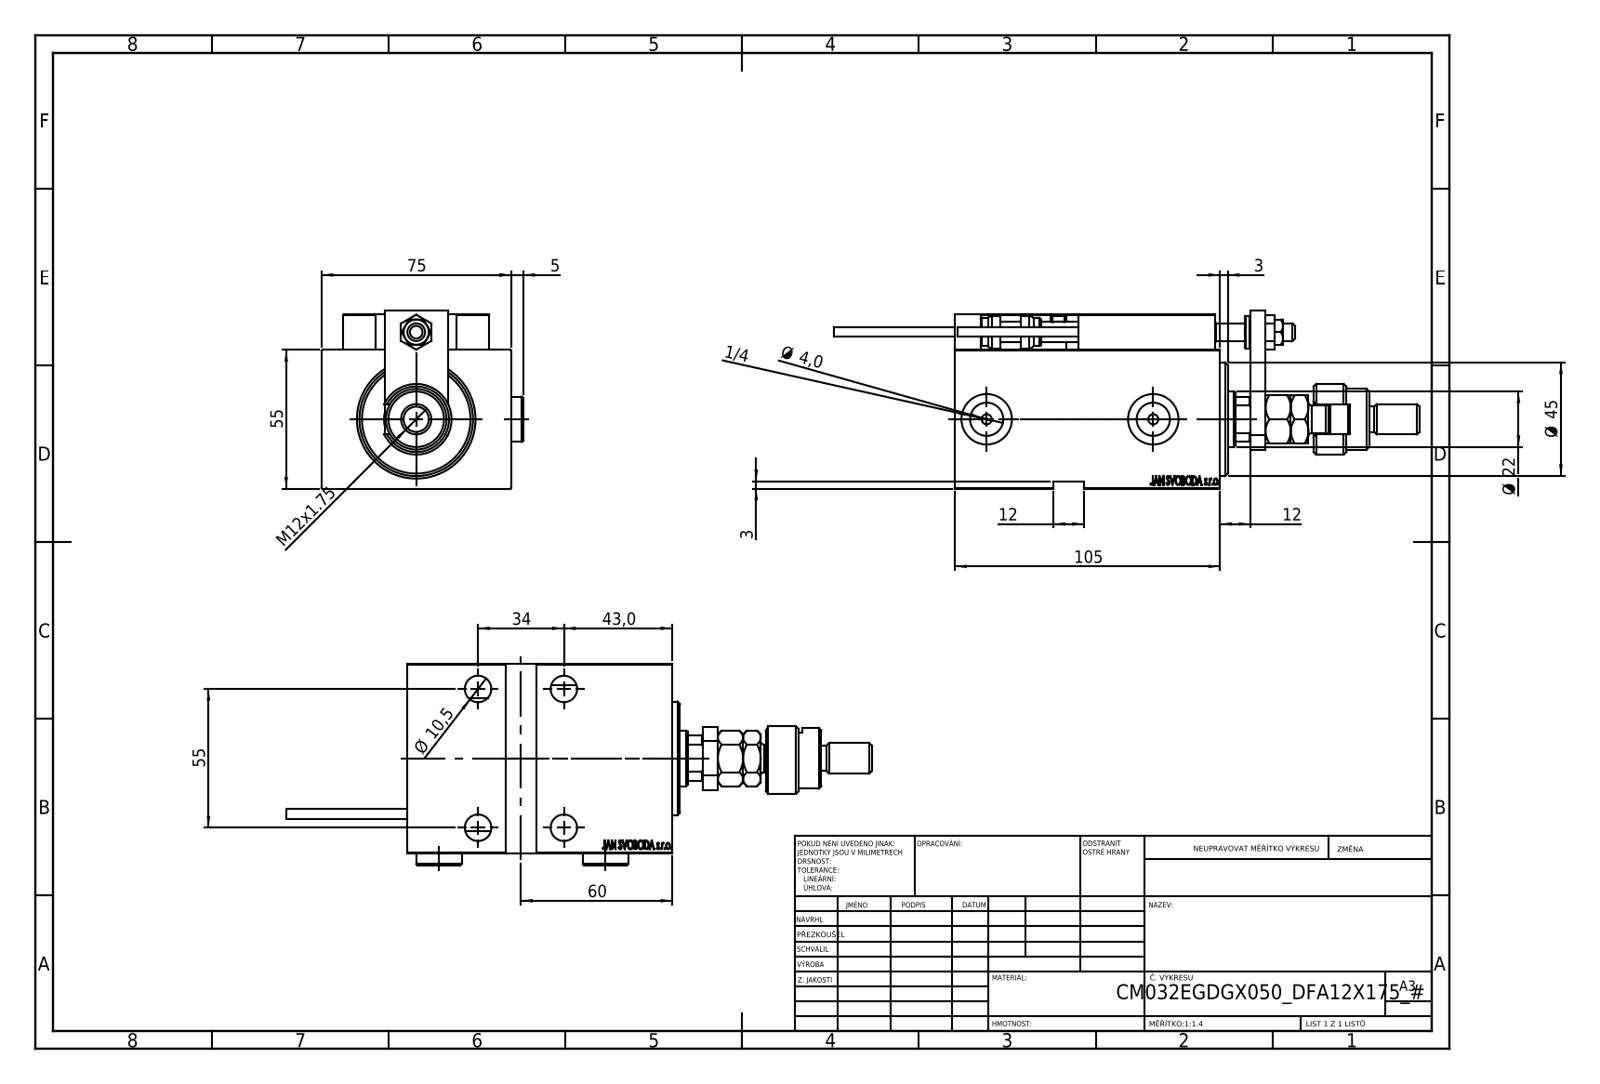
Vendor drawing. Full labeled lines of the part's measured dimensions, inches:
Part name (STEP PRODUCT): V450CM_E_Body; SWITCH X; SWITCH_X_FRONT_BACK; FEMALE_PART_FOR_DFA (+7 more)
STEP written by: SolidWorks 2019 (CONFIG_CONTROL_DESIGN)
Units: inches
Bodies: 28 solids, 1431 faces (633 planar, 209 cylindrical, 589 other)
Overall size (bounding box): 9.134 × 3.146 × 2.776
Volume: 27.63 in³ · Surface area: 165.2 in²
Round holes (diameter × count): ⌀0.157 ×6, ⌀0.315 ×5, ⌀0.413 ×5, ⌀0.65 ×5, ⌀0.126 ×4, ⌀0.197 ×2, ⌀0.518 ×2, ⌀0.787 ×2, ⌀0.276 ×1, ⌀0.866 ×1, ⌀1.004 ×1, ⌀1.26 ×1
Round bosses / shafts (diameter × count): ⌀0.709 ×3, ⌀0.433 ×2, ⌀0.197 ×2, ⌀0.15 ×2, ⌀1.339 ×1, ⌀1.102 ×1, ⌀0.945 ×1, ⌀0.512 ×1
Partial cylindrical surfaces — rounded edges, fillets, slot ends (radius × count): R0.012 ×30, R0.118 ×2, R0.384 ×1, R0.413 ×1
Main face-to-face distances: 2.165, 2.953, 0.118, 0.394, 0.551, 4.134, 0.197, 2.717, 0.472, 0.709
Hole centre spacings: 0.448, 0.787, 1.138, 1.165, 1.169, 1.339, 1.42, 1.576
